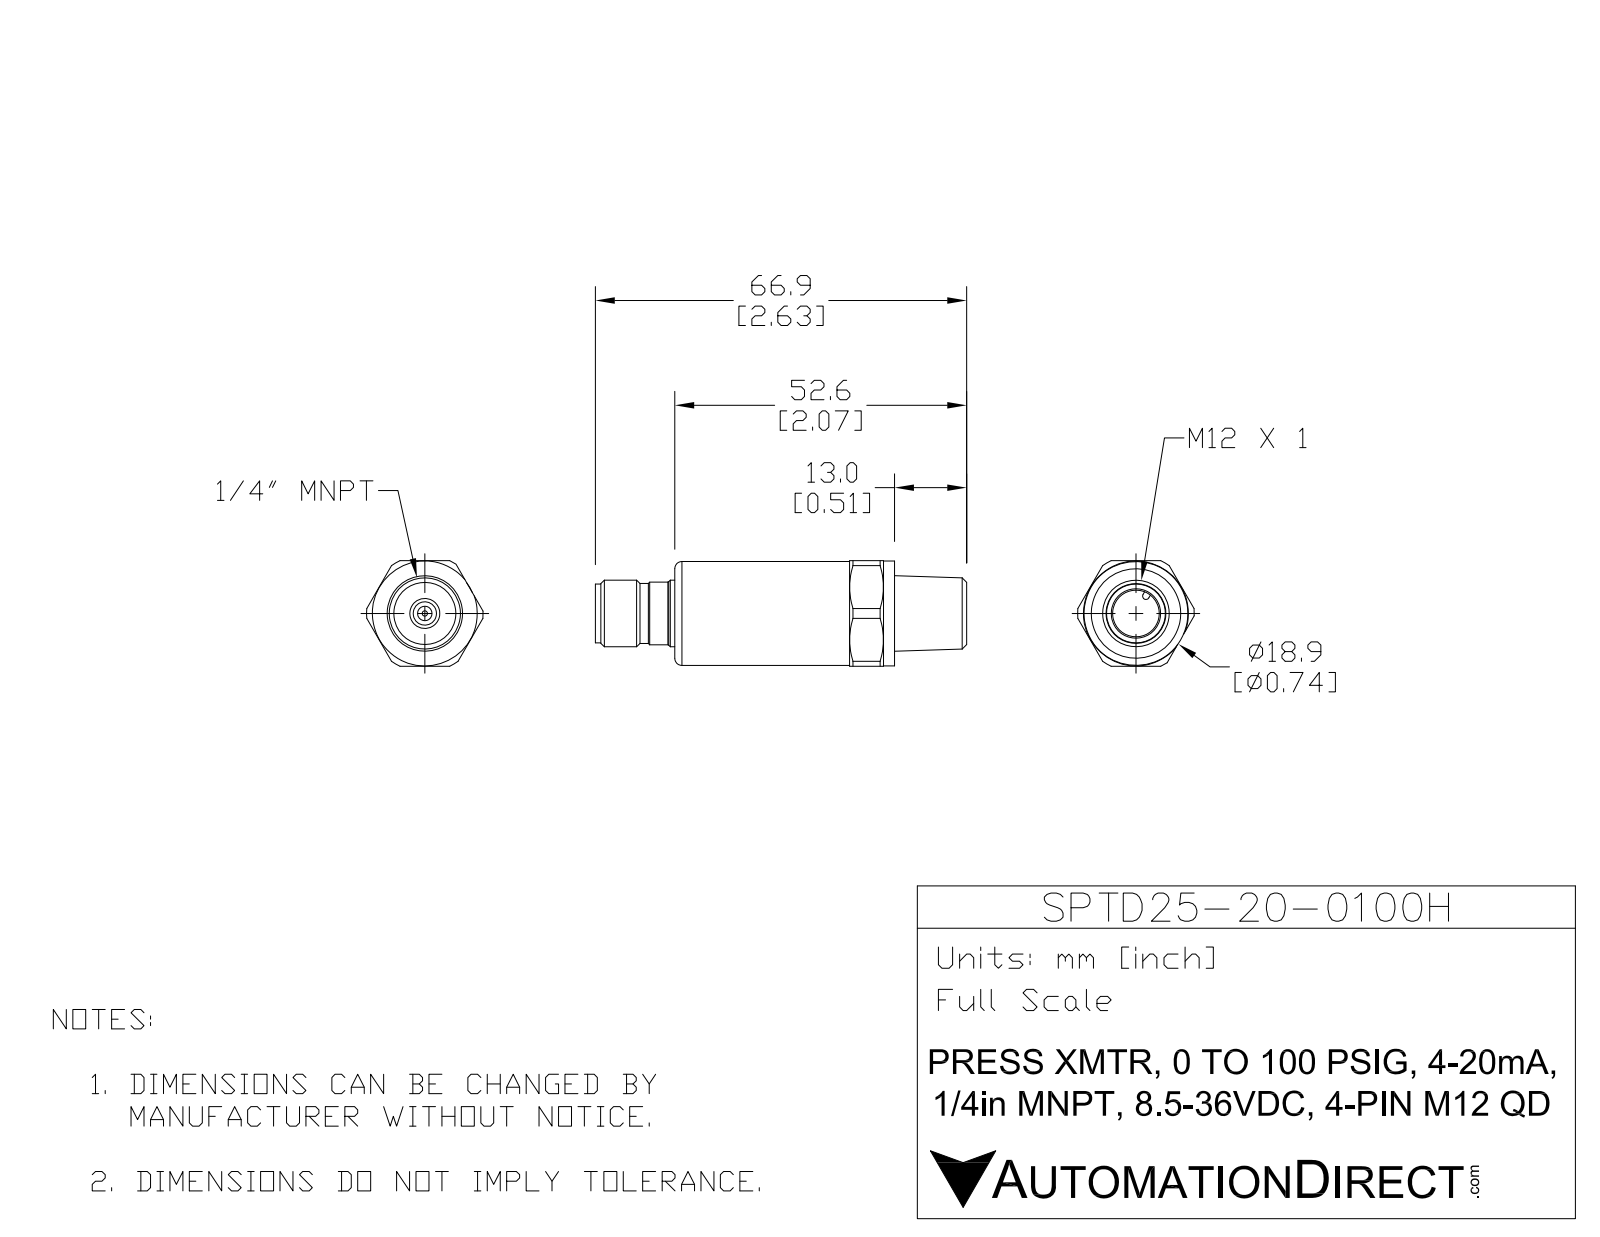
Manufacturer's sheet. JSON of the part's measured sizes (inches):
{"part_name": "SPDT25-20-0100H", "step_written_by": "SolidWorks 2015 (AUTOMOTIVE_DESIGN)", "units": "inches", "bodies": {"solids": 7, "faces": 177, "planar": 44, "cylindrical": 53, "other": 80}, "overall_size": [2.634, 0.849, 0.744], "volume_in3": 0.821, "surface_area_in2": 8.272, "round_holes": [[0.165, 1], [0.331, 1], [0.654, 1]], "round_bosses_or_shafts": [[0.055, 4], [0.039, 4], [0.744, 1], [0.472, 1], [0.445, 1], [0.425, 1], [0.417, 1], [0.413, 1]], "partial_cylinders_radius": [[0.024, 1]], "face_to_face_distances": [0.744, 2.069, 0.515, 1.554, 2.287, 1.772, 0.219, 0.563, 0.047, 1.506]}
